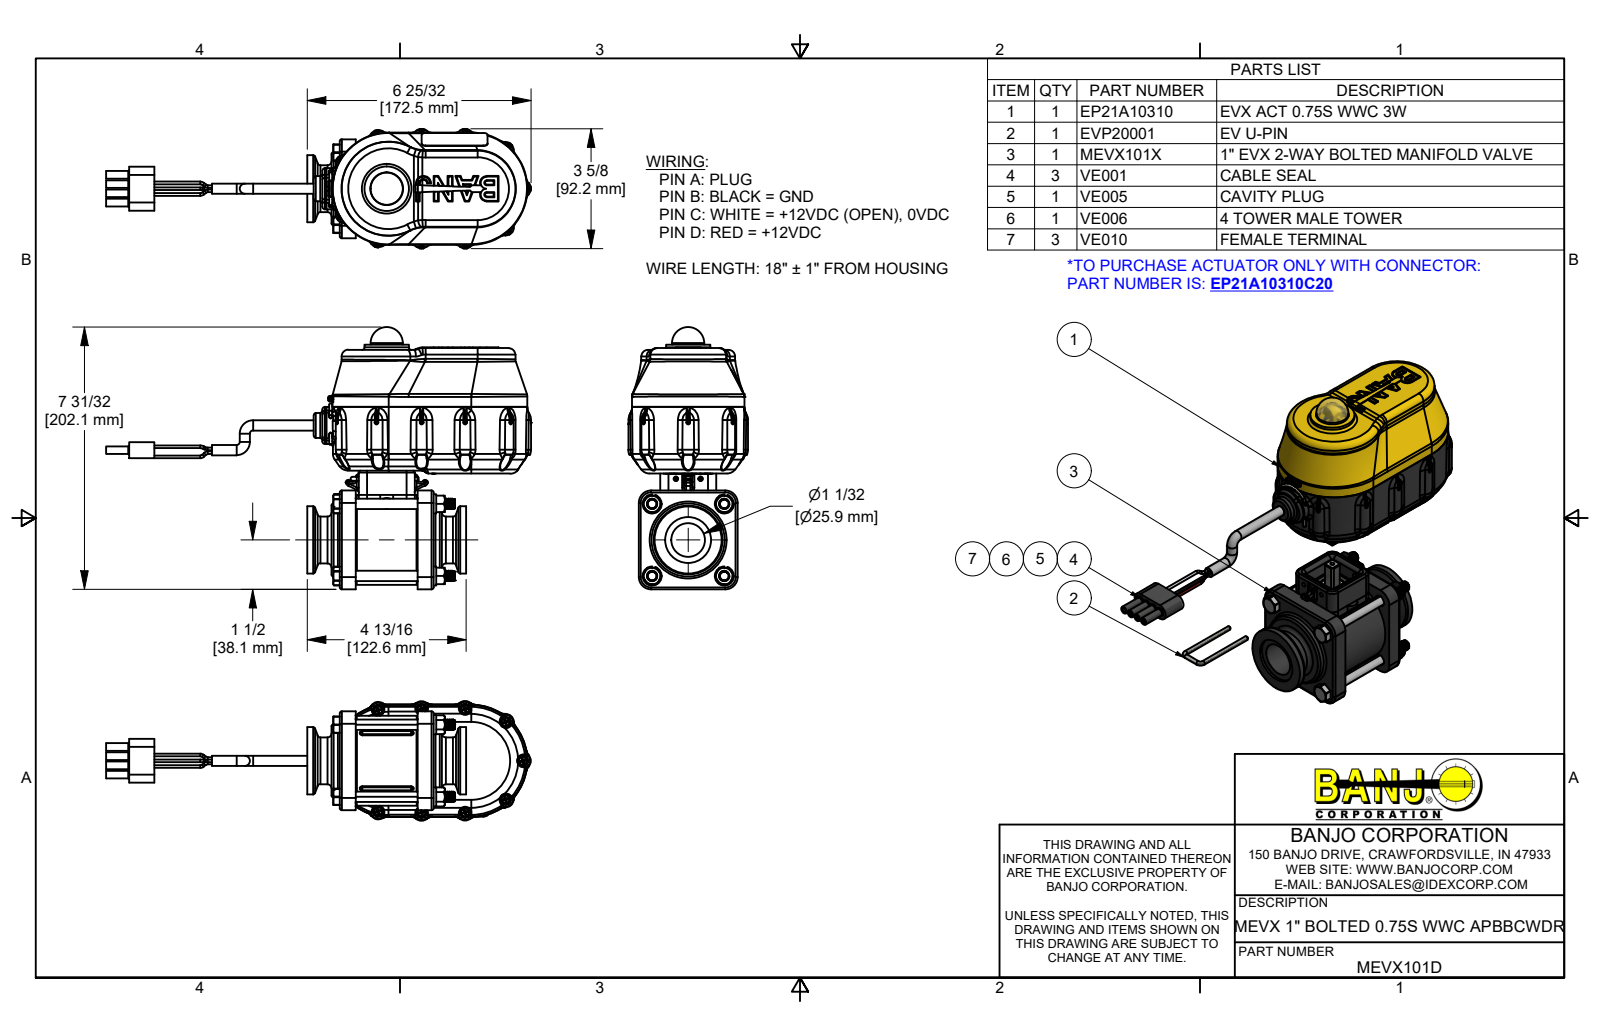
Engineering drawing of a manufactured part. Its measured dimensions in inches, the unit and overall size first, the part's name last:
Units: inches
Overall size (bounding box): 12.901 × 7.957 × 3.63
Round holes (diameter × count): ⌀0.095 ×11, ⌀0.15 ×11, ⌀0.08 ×7, ⌀0.107 ×4, ⌀0.126 ×4, ⌀0.135 ×4, ⌀0.136 ×4, ⌀0.14 ×4, ⌀0.148 ×4, ⌀0.15 ×4, ⌀0.17 ×4, ⌀0.243 ×4
Round bosses / shafts (diameter × count): ⌀0.268 ×60, ⌀0.25 ×17, ⌀0.08 ×15, ⌀0.14 ×11, ⌀0.108 ×11, ⌀0.085 ×11, ⌀0.058 ×6, ⌀0.313 ×5
Partial cylindrical surfaces — rounded edges, fillets, slot ends (radius × count): R0.013 ×180, R0.04 ×145, R0.01 ×94, R0.02 ×94, R0.005 ×57, R0.03 ×47, R0.06 ×42, R0.015 ×33
Main face-to-face distances: 0.1, 2.565, 0.48, 0.211, 0.06, 0.151, 0.055, 2.365, 0.125, 1.896
Hole centre spacings: 0.87, 0.9, 1.547, 1.662, 1.891, 2.188, 2.656, 2.69
Volume: 51.57 in³ · Surface area: 605.1 in²
Bodies: 104 solids, 11709 faces (2920 planar, 3557 cylindrical, 5232 other)
Part name (STEP PRODUCT): MEVX101D; EP21A10310; EP10310; IRF4905 (+8 more)
STEP written by: Autodesk Inventor 2021 (AUTOMOTIVE_DESIGN)
